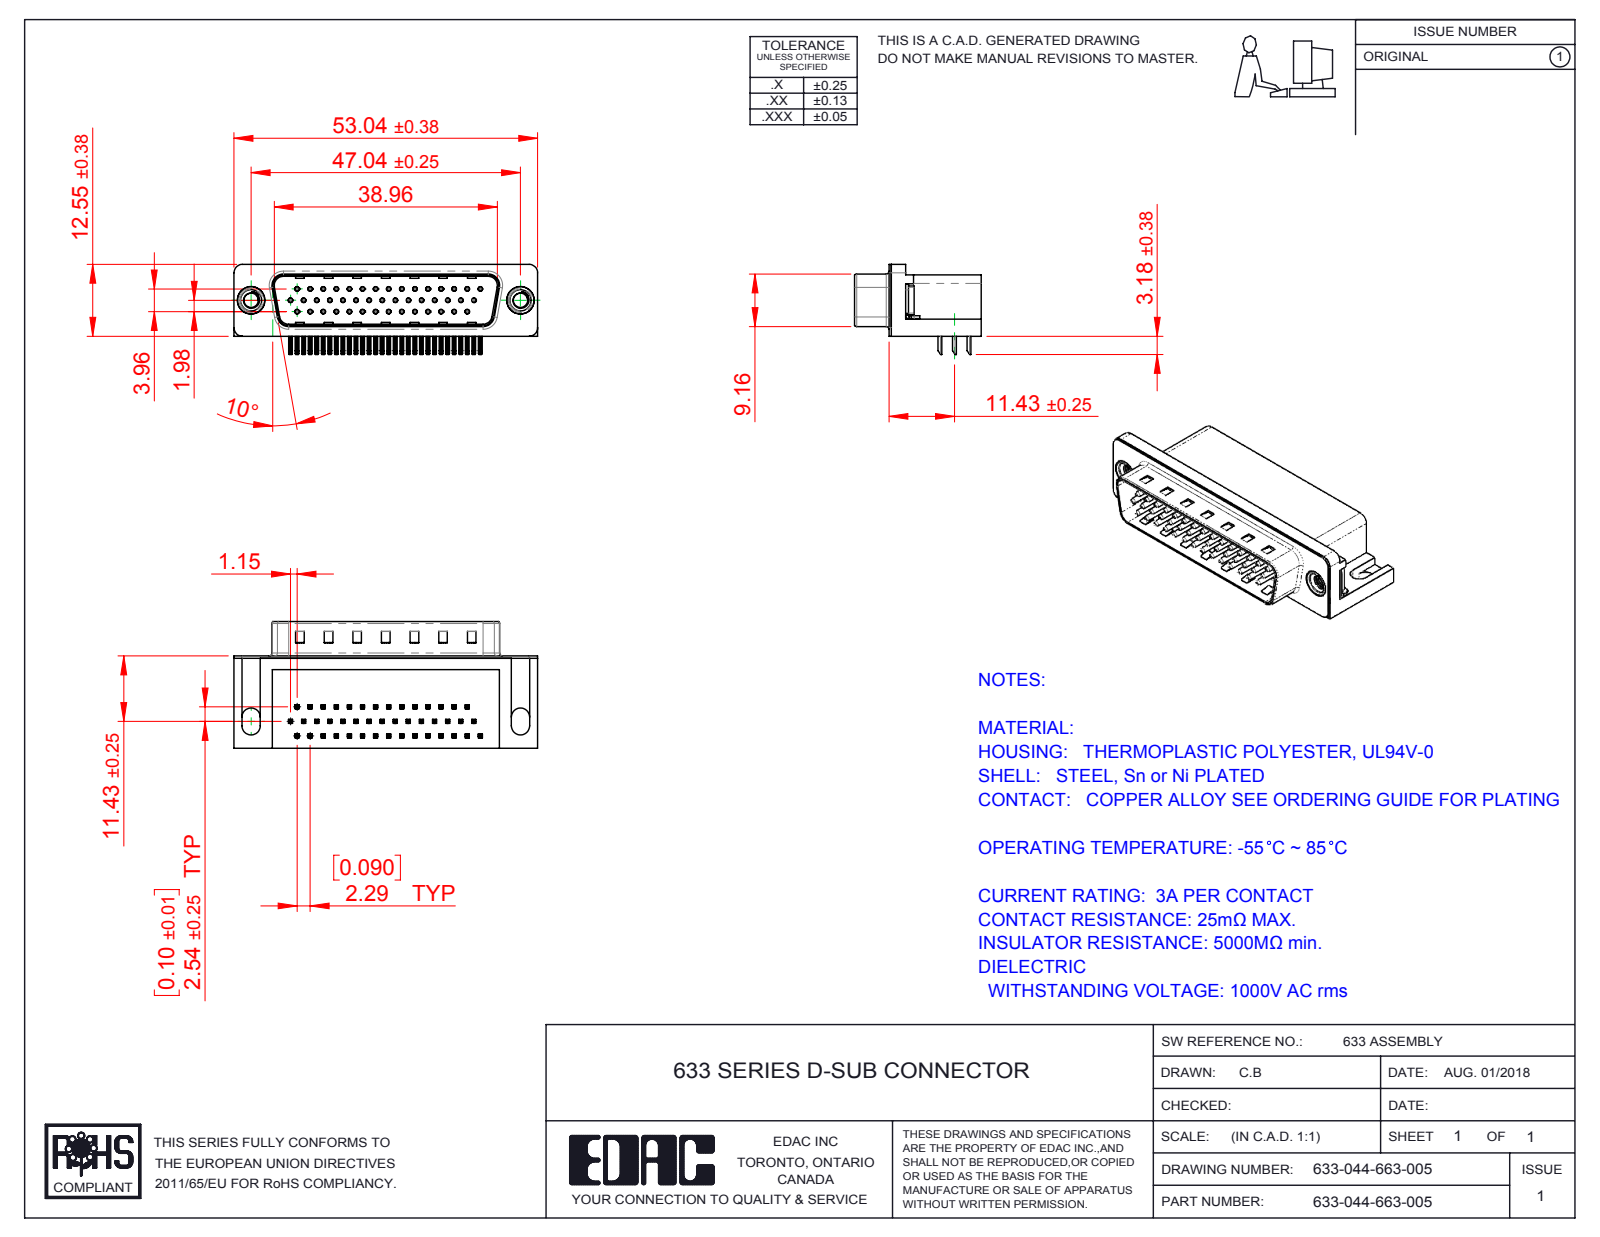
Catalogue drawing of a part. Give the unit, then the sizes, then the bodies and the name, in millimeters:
Units: millimetres
Overall size (bounding box): 53.04 × 22.1 × 15.73
Round holes (diameter × count): ⌀0.35 ×44, ⌀0.8 ×44, ⌀2.5 ×2, ⌀4 ×2, ⌀4.8 ×2, ⌀5 ×2
Round bosses / shafts (diameter × count): ⌀0.75 ×44, ⌀4.9 ×2, ⌀4.75 ×2, ⌀3.9 ×2
Partial cylindrical surfaces — rounded edges, fillets, slot ends (radius × count): R0.25 ×184, R0.12 ×88, R1 ×16, R0.5 ×9, R1.6 ×8, R1.5 ×7, R0.9 ×4, R2 ×4
Main face-to-face distances: 0.4, 10.35, 15.7, 8.76, 2.9, 2.5, 2.1, 16.1, 10.7, 2.54
Hole centre spacings: 2.29, 4.57, 4.58, 2.28, 6.87, 9.16, 11.45, 2.27
Volume: 8 062 mm³ · Surface area: 9 999 mm²
Bodies: 50 solids, 3686 faces (2317 planar, 1060 cylindrical, 309 other)
Part name (STEP PRODUCT): 633-044-663-005; 633 Housing_44 Contact; 633 Shell_44 Contact; 633 M3 Threaded Rivet (+4 more)
STEP written by: SolidWorks 2016 (CONFIG_CONTROL_DESIGN)
